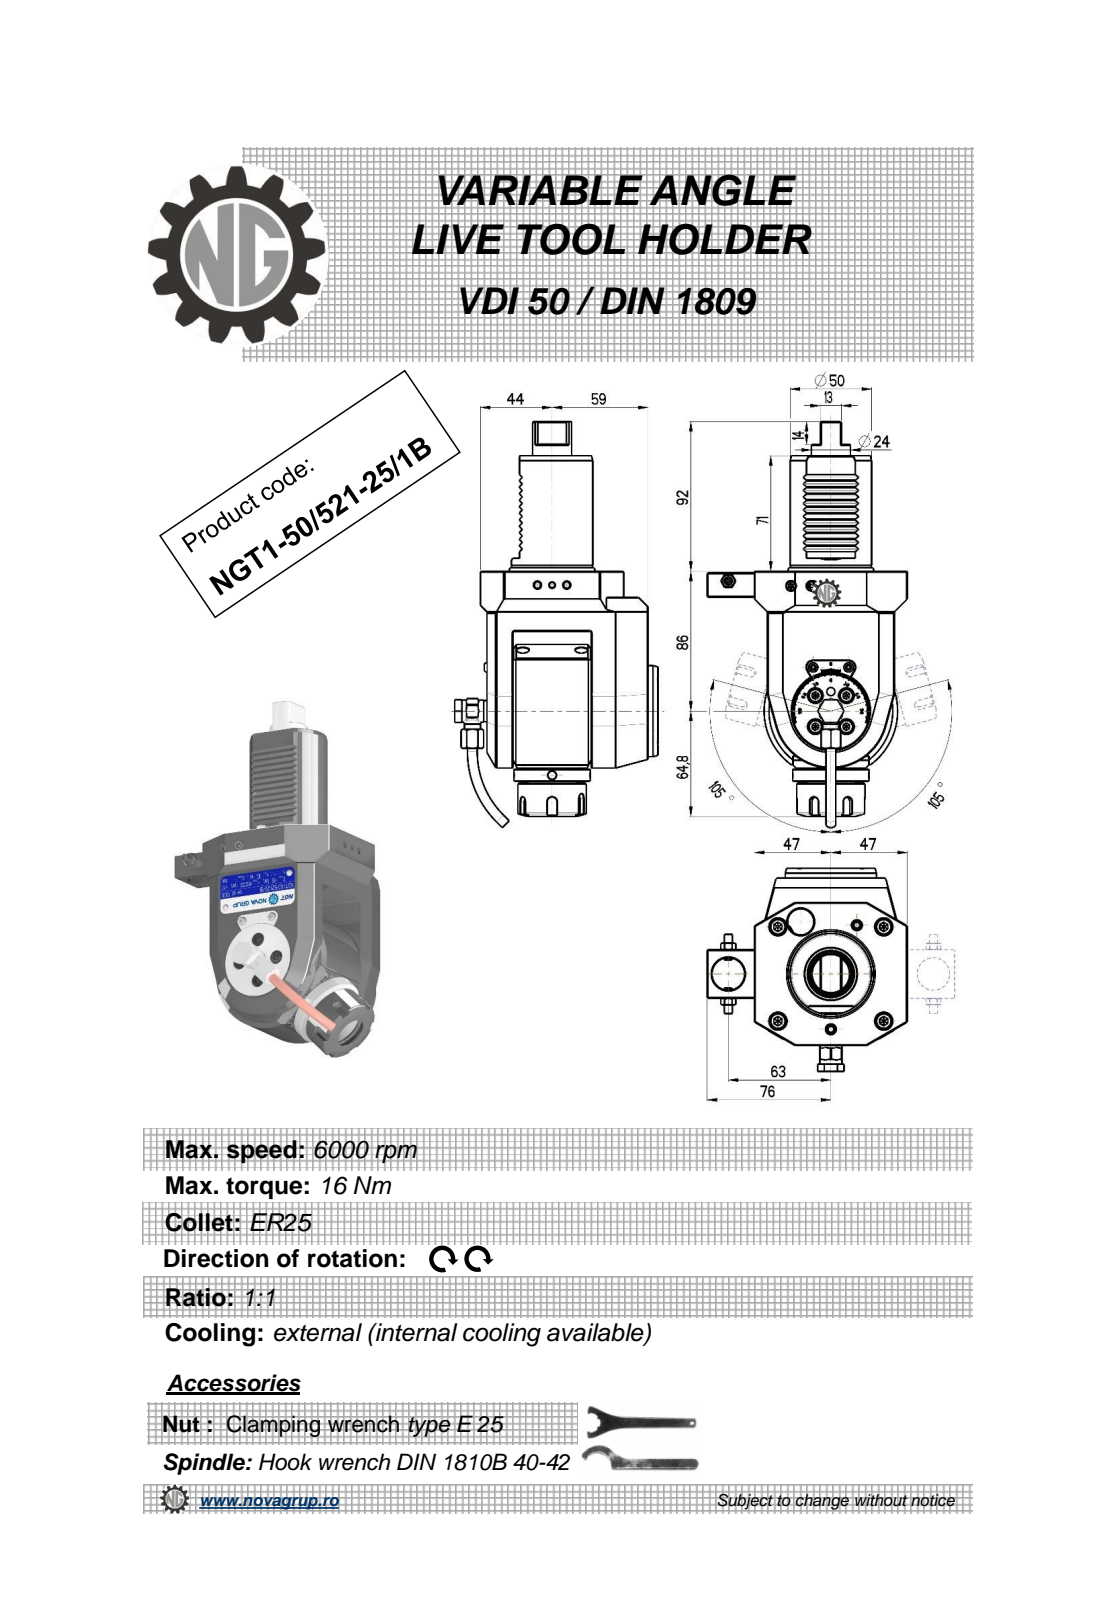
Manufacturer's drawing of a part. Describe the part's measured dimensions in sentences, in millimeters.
The part is named "NGT1_50_521_25_1B". Its 3-D file was written by "PRO/ENGINEER BY PARAMETRIC TECHNOLOGY CORPORATION, 2010280 (CONFIG_CONTROL_DESIGN)". It is 1 solid with 616 faces: 269 planar, 146 cylindrical and 201 other. Overall it measures 249.67 by 124.9 by 123 millimeters. Its volume is 1 012 000 cubic millimeters and its surface area 90 875 square millimeters. Round holes: 5 of diameter 4, 2 of diameter 3.8, 2 of diameter 5, 1 of diameter 3, 1 of diameter 6.2, 1 of diameter 9, 1 of diameter 9.5, 1 of diameter 10, 1 of diameter 11, 1 of diameter 20, 1 of diameter 20.3. Round bosses or shafts: 2 of diameter 6, 2 of diameter 5.7, 1 of diameter 82, 1 of diameter 56, 1 of diameter 50, 1 of diameter 47, 1 of diameter 42, 1 of diameter 35. Partial cylindrical surfaces (rounded edges, fillets, slot ends): 12 of radius 0.26, 12 of radius 0.3, 6 of radius 0.16, 5 of radius 3, 4 of radius 0.5, 2 of radius 0.8, 2 of radius 1, 2 of radius 10. The main face-to-face distances are 37, 99, 16, 8, 21, 6, 64, 105, 20, 35. The hole center spacings are 9, 117.3, 0.4, 18, 39.45, 49, 49.4, 63.
